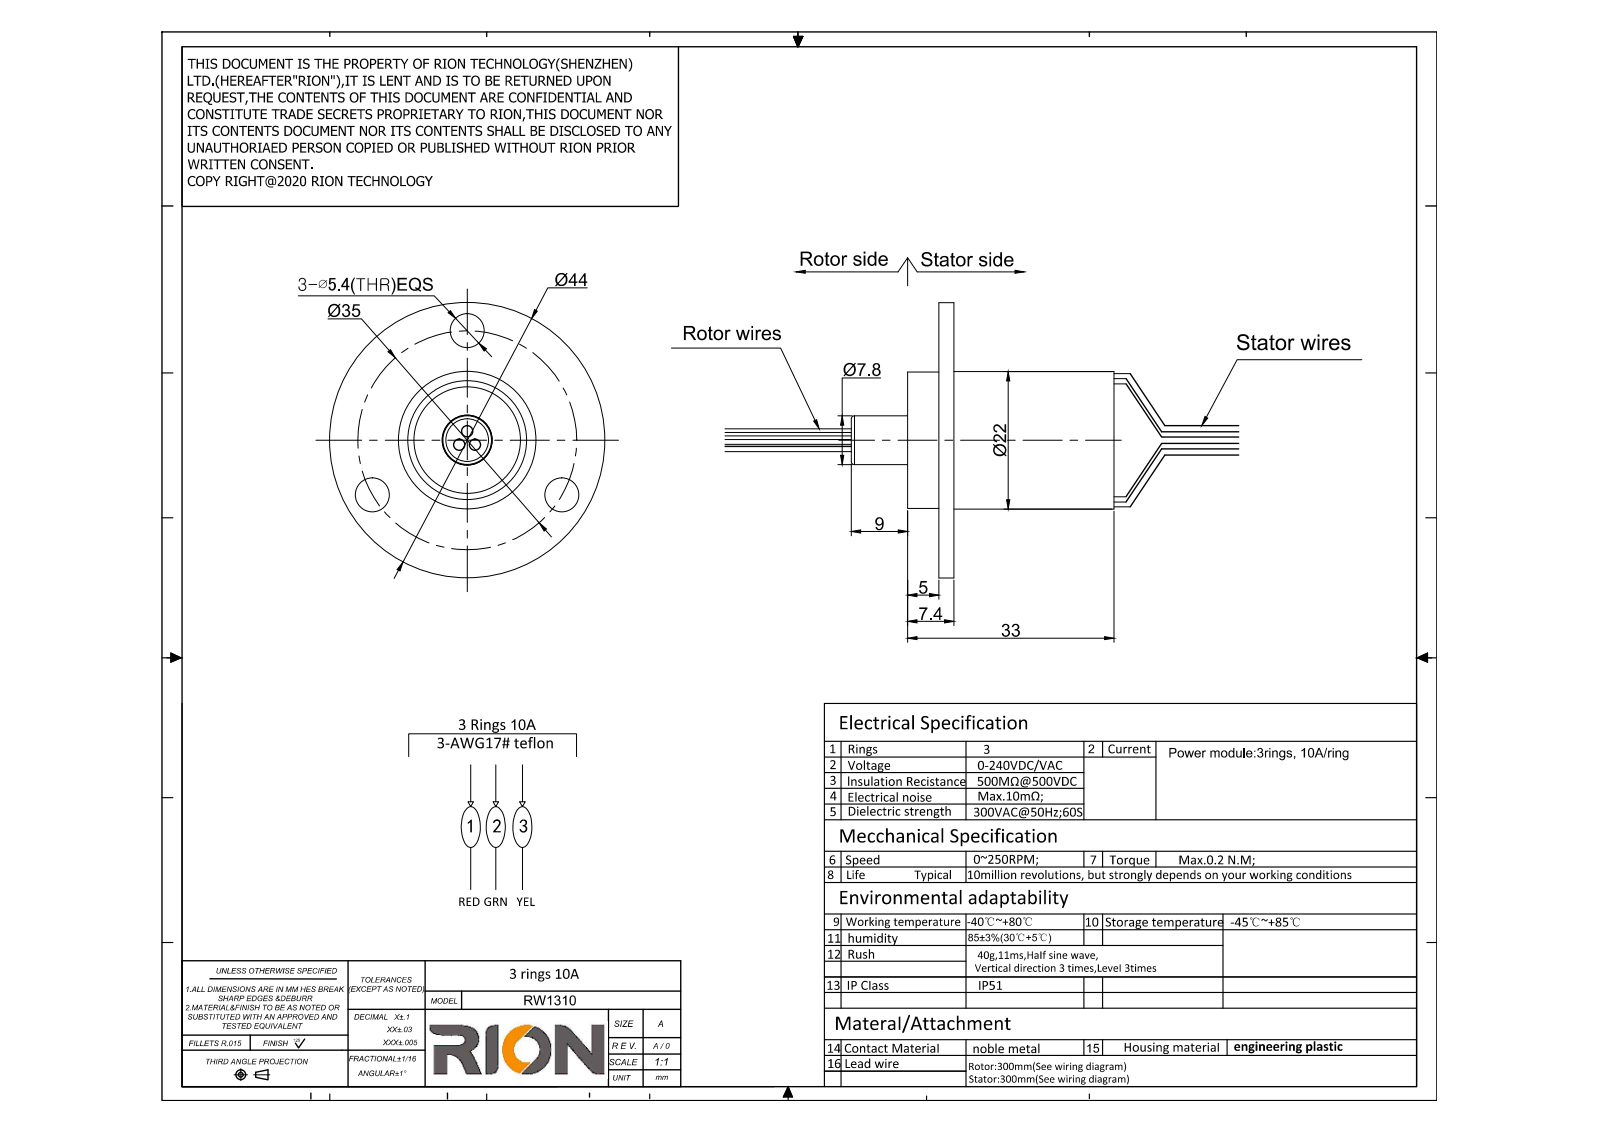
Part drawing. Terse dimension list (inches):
name: MW1310
written by: SolidWorks 2014 (CONFIG_CONTROL_DESIGN)
unit: in
bodies: 1 solid, 66 faces (26 planar, 38 cylindrical, 2 other)
size: 3.185 × 1.732 × 1.732
volume: 0.979 in³; area: 10.22 in²
holes: 3× ⌀0.213, 1× ⌀0.157, 1× ⌀0.276, 1× ⌀0.787
bosses: 6× ⌀0.071, 1× ⌀1.732, 1× ⌀0.874, 1× ⌀0.783, 1× ⌀0.307, 1× ⌀0.268
face distances: 0.094, 1.102, 1.008, 0.197, 0.291, 1.299, 0.354, 0.551, 0.646, 1.654
hole spacings: 0.689, 1.193, 1.194
